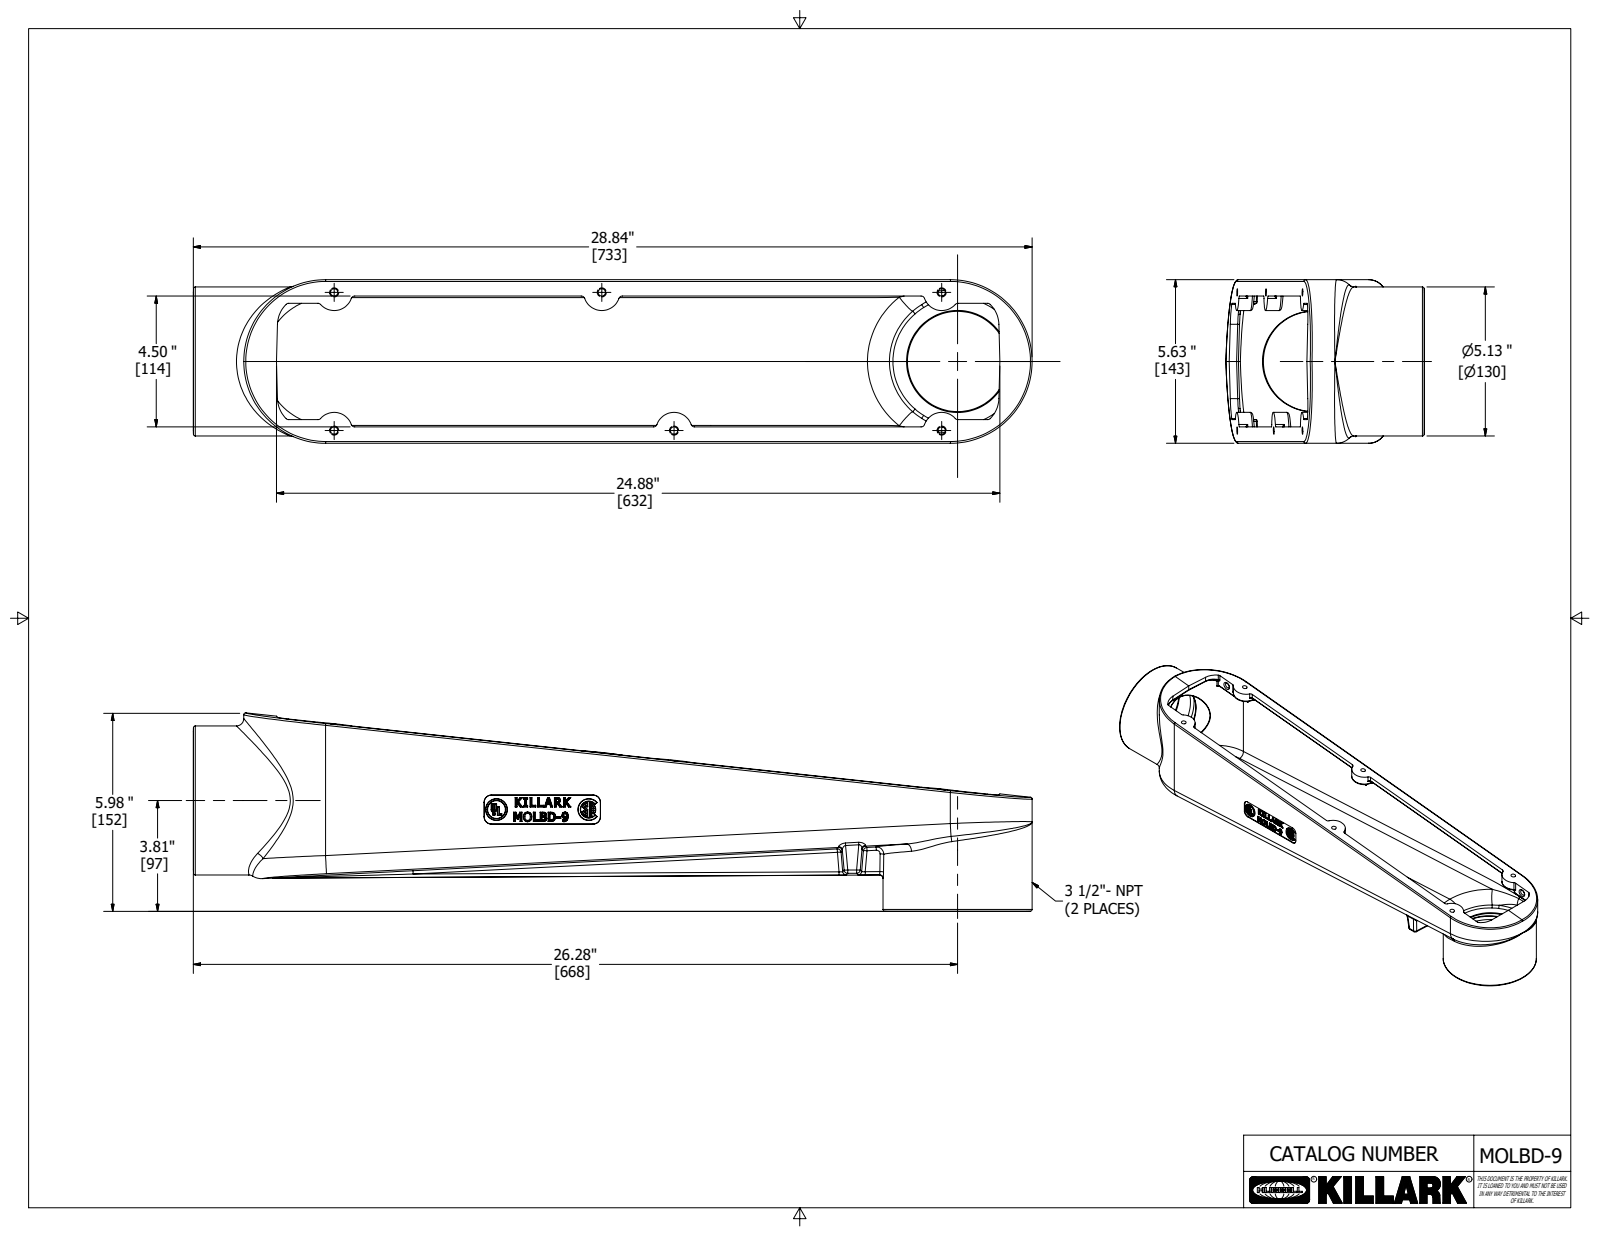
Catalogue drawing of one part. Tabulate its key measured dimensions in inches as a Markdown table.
| quantity | value |
| --- | --- |
| part name | 21030-2 |
| STEP written by | Autodesk Inventor 2020 (AUTOMOTIVE_DESIGN) |
| units | inches |
| bodies | 1 solid, 856 faces (300 planar, 152 cylindrical, 404 other) |
| overall size | 28.844 × 6.824 × 5.625 |
| volume | 147.3 in³ |
| surface area | 822.9 in² |
| round holes (diameter × count) | 0.252 × 6, 3.448 × 2, 4.011 × 2 |
| round bosses / shafts (diameter × count) | 5.125 × 2 |
| partial cylindrical surfaces (radius × count) | 0.125 × 44, 0.062 × 36, 0.031 × 12, 0.625 × 8, 0.171 × 6, 0.033 × 4, 1 × 4, 2.437 × 2 |
| main face-to-face distances | 0.313, 5.313, 0.312, 5.625, 5, 0.25, 0.563, 5.063, 4.75, 0.271 |
| hole center spacings | 2.437, 4.75, 9.203, 10.356, 11.687, 12.616, 20.891, 21.424 |
